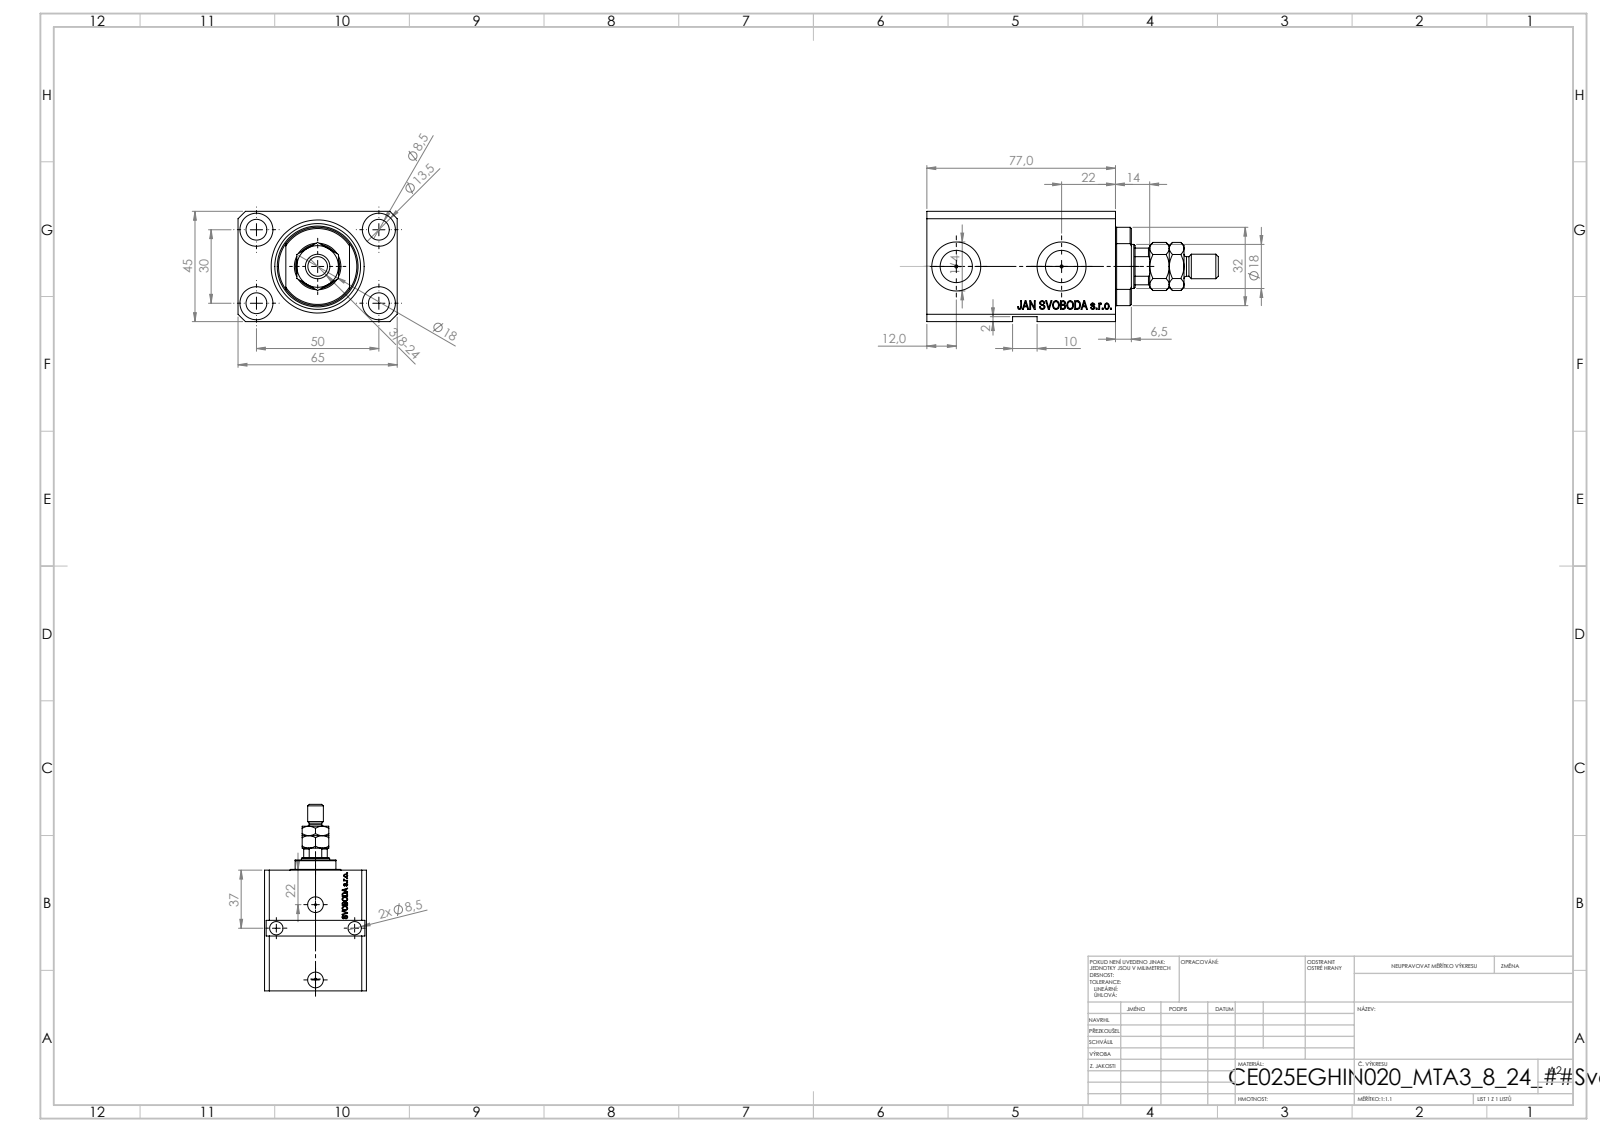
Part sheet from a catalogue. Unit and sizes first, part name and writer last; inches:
Units: inches
Overall size (bounding box): 4.685 × 2.559 × 1.772
Round holes (diameter × count): ⌀0.335 ×7, ⌀0.049 ×4, ⌀0.531 ×4, ⌀0.394 ×2, ⌀0.518 ×2, ⌀0.787 ×2, ⌀0.709 ×1, ⌀0.984 ×1, ⌀1.496 ×1
Round bosses / shafts (diameter × count): ⌀0.394 ×1, ⌀0.315 ×1
Partial cylindrical surfaces — rounded edges, fillets, slot ends (radius × count): R0.335 ×1, R0.63 ×1
Main face-to-face distances: 1.772, 2.559, 0.551, 2.48, 3.031, 0.272, 2.209, 2.76, 1.693, 1.102
Hole centre spacings: 1.148, 1.969, 1.181, 1.613, 1.63, 2.296, 0.021, 1.693
Volume: 11.97 in³ · Surface area: 83.7 in²
Bodies: 4 solids, 946 faces (450 planar, 88 cylindrical, 408 other)
Part name (STEP PRODUCT): V250CE_C_VCP; V250CE_E_Body; MTA; V250CE_VC_E
STEP written by: SolidWorks 2019 (CONFIG_CONTROL_DESIGN)
